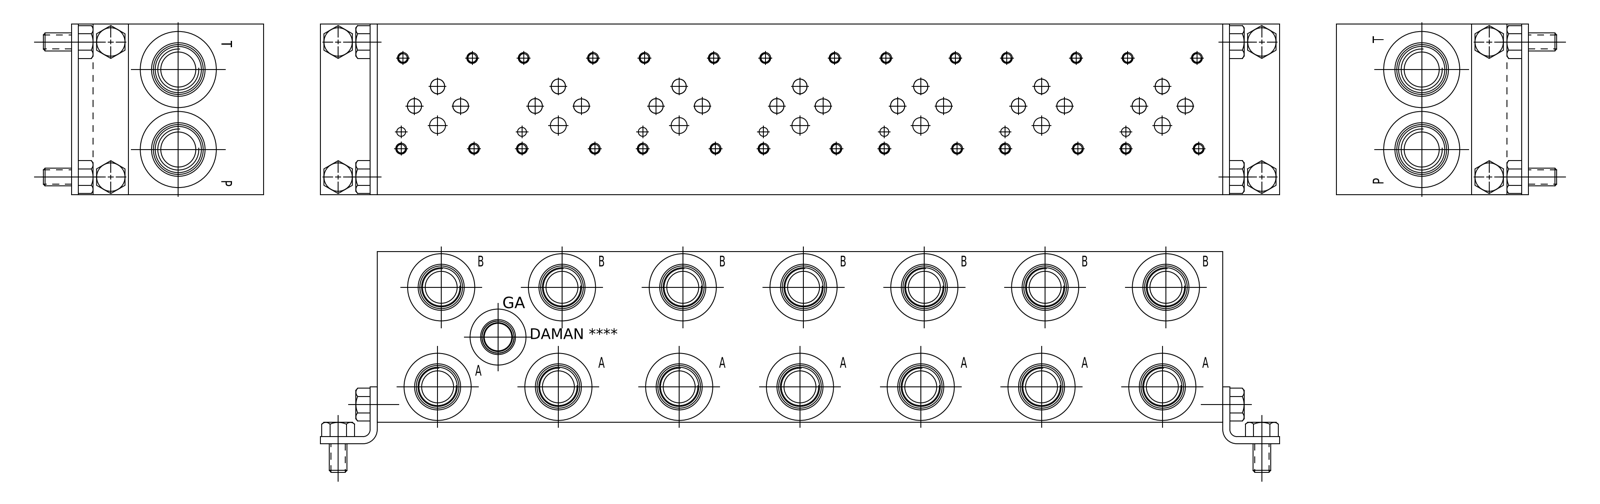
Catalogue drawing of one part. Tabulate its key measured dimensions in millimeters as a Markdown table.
| quantity | value |
| --- | --- |
| part name | Part_AD03S072S_3D |
| STEP written by | Autodesk Inventor 2019 (AUTOMOTIVE_DESIGN) |
| units | millimeters |
| bodies | 1 solid, 1090 faces (517 planar, 197 cylindrical, 376 other) |
| overall size | 377.82 × 76.2 × 76.2 |
| volume | 2 043 000 mm³ |
| surface area | 165 819 mm² |
| round holes (diameter × count) | 3.78 × 28, 4.83 × 28, 6.35 × 21, 14.3 × 14, 17.5 × 14, 19.05 × 14, 19.25 × 14, 30.63 × 14, 3.96 × 7, 7.14 × 7, 6.53 × 2, 7.92 × 2 |
| main face-to-face distances | 76.2, 0.79, 75.41, 377.82, 377.03, 377.04, 376.25, 0.78, 15.06, 14.27 |
| hole center spacings | 107.95, 53.97, 53.98, 215.9, 161.92, 161.93, 98, 98.03 |
